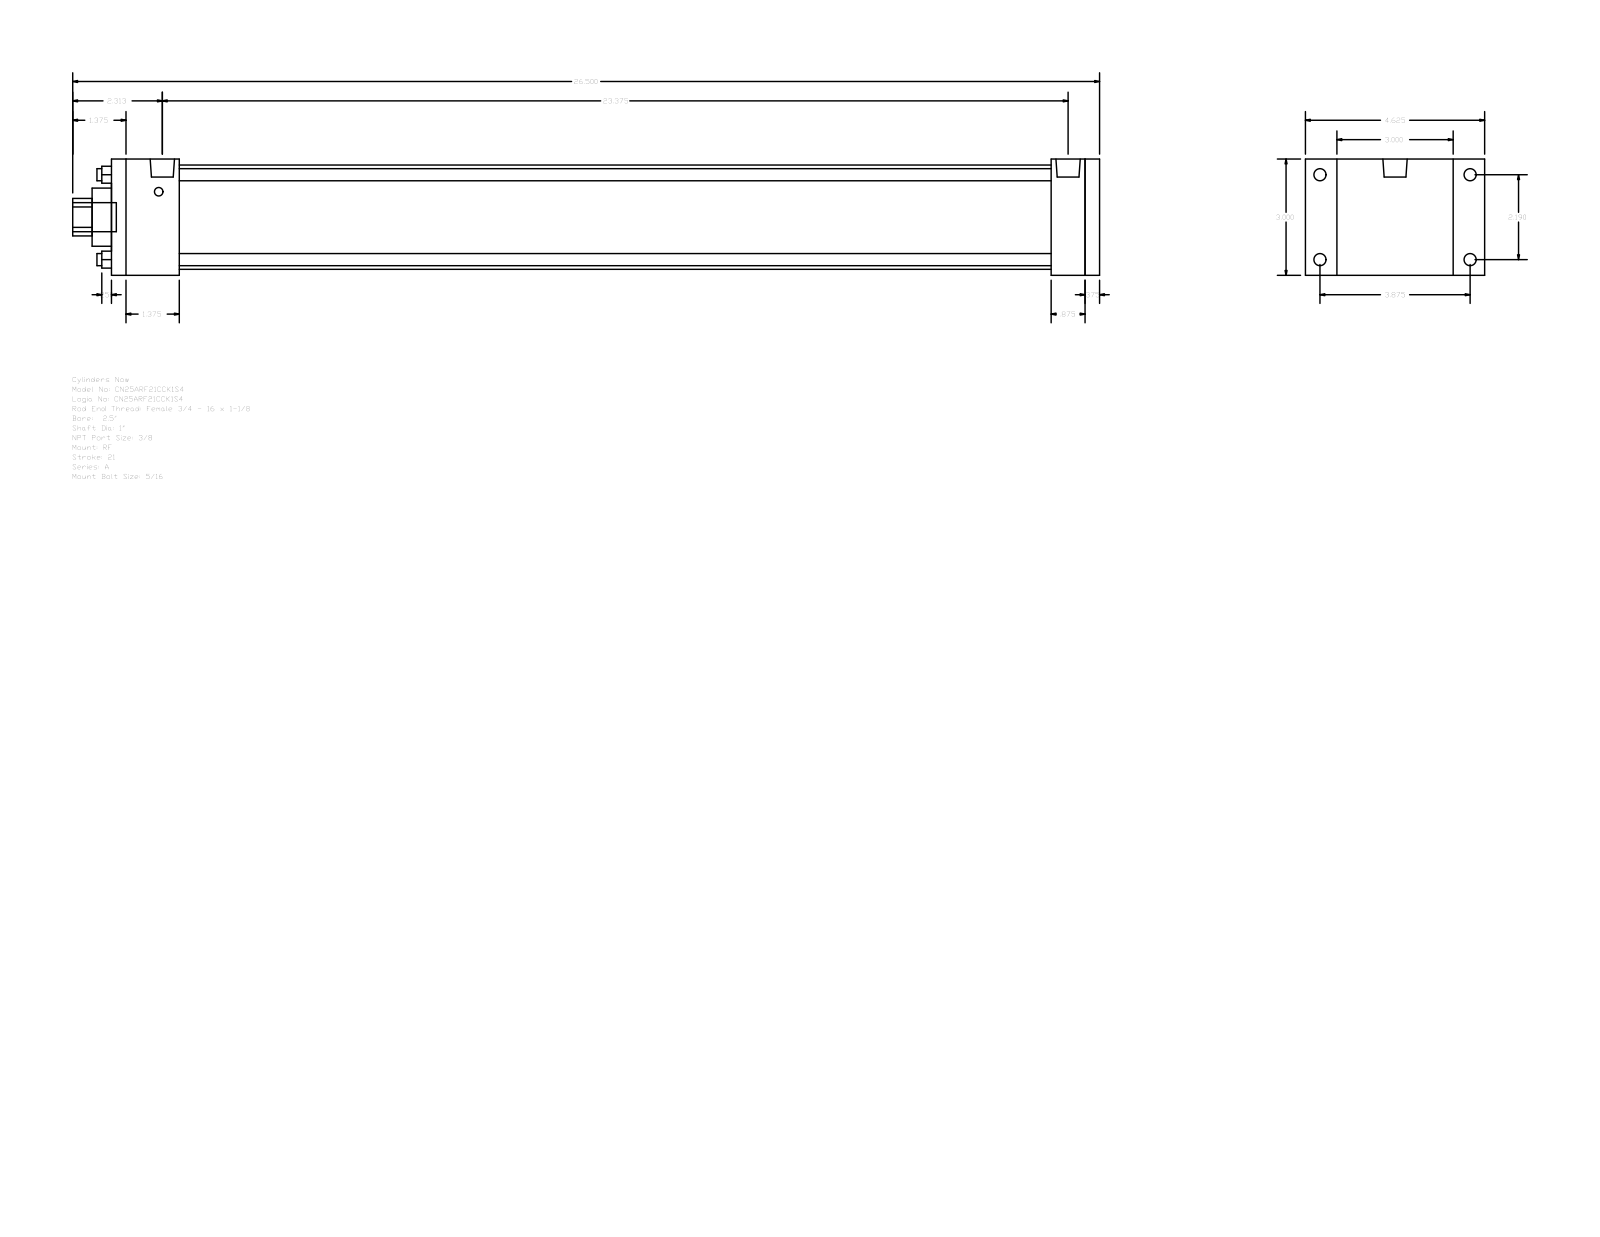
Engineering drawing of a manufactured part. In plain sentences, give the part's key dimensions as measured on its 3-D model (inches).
The part is named "A_RF__0250_1". Its 3-D file was written by "GSSL Pune (CONFIG_CONTROL_DESIGN)". It is 0 solids with 92 faces: 64 planar, 28 cylindrical and 0 other. Overall it measures 26.5 by 4.625 by 3 inches. Round holes: 4 of diameter 0.313, 1 of diameter 1, 1 of diameter 1.5, 1 of diameter 2.69. Round bosses or shafts: 4 of diameter 0.313, 4 of diameter 0.219, 2 of diameter 0.627, 1 of diameter 0.75. Partial cylindrical surfaces (rounded edges, fillets, slot ends): 1 of radius 0.484. The main face-to-face distances are 3, 25.5, 0.375, 25.125, 1.75, 24.25, 22.5, 23.375, 23.75, 0.875. The hole center spacings are 1.548, 2.19, 3.097.
